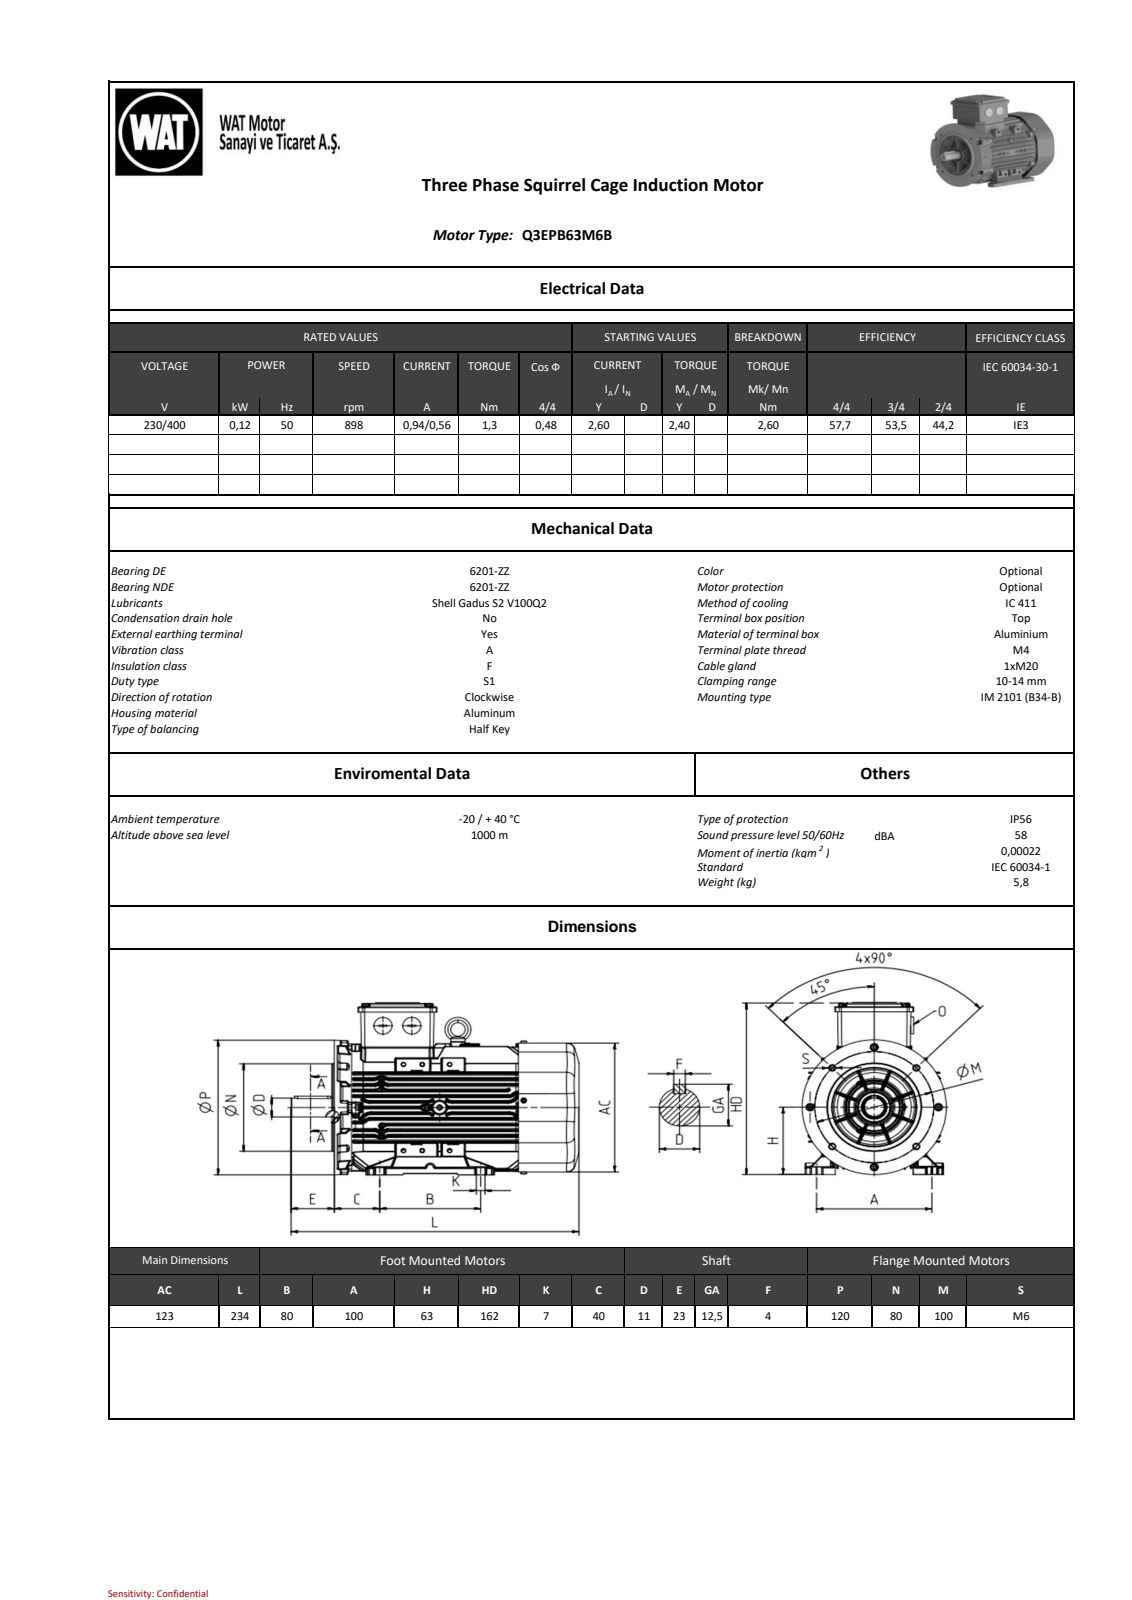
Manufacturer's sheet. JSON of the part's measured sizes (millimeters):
{"part_name": "QE Series_ 63_B34b_Deep Cover__stp_objects", "step_written_by": "SIEMENS PLM Software NX2206.8101 (AP203_CONFIGURATION_CONTROLLED_3D_DESIGN_OF_MECHANICAL_PARTS_AND_ASSEMBLIES_MIM_LF)", "units": "millimeters", "bodies": {"solids": 0, "faces": 1554, "planar": 845, "cylindrical": 465, "other": 244}, "overall_size": [233.47, 162.1, 126.28], "round_holes": [[2.5, 4], [3.65, 4], [4.2, 4], [6, 4], [3, 3], [7, 2], [5, 1], [8, 1], [14.96, 1], [19, 1], [19.84, 1], [57, 1]], "round_bosses_or_shafts": [[8, 8], [4.8, 4], [4, 3], [123, 1], [120, 1], [80, 1], [61, 1], [25.28, 1]], "partial_cylinders_radius": [[1, 109], [0.5, 108], [2, 35], [1.5, 16], [4, 8], [8, 7], [0.1, 5], [0.3, 5]], "face_to_face_distances": [5, 7.02, 27.96, 28.05, 10.5, 6.93, 13.81, 6.88, 181.5, 1], "hole_center_spacings": [54, 70.71, 10, 50, 5, 31.5, 31.52, 31.89]}
